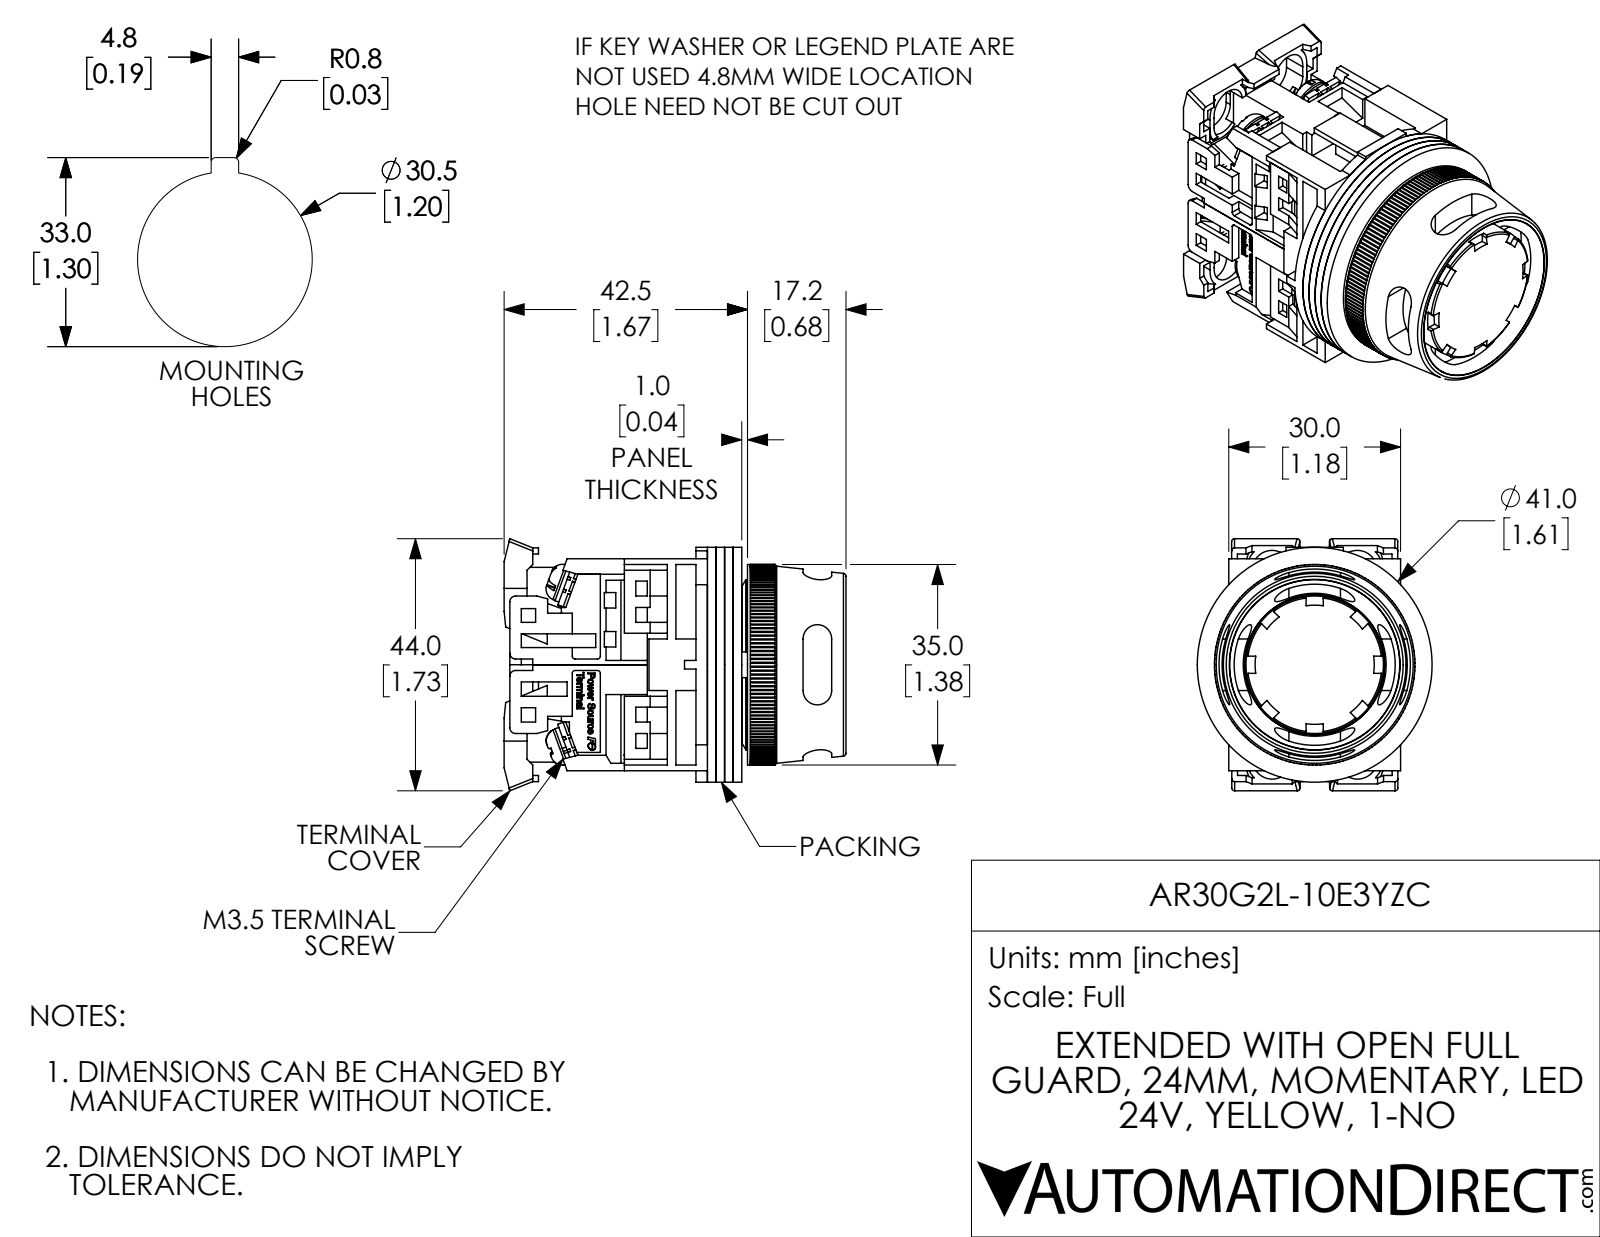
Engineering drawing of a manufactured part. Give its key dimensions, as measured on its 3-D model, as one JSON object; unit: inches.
{"part_name": "AR30G2L-10E3YZC", "step_written_by": "SolidWorks 2017 (AUTOMOTIVE_DESIGN)", "units": "inches", "bodies": {"solids": 25, "faces": 2179, "planar": 1508, "cylindrical": 458, "other": 213}, "overall_size": [2.35, 1.732, 1.614], "volume_in3": 2.142, "surface_area_in2": 62.62, "round_holes": [[0.138, 8], [0.142, 4], [0.118, 1], [0.472, 1], [0.709, 1], [0.728, 1], [0.787, 1], [0.945, 1], [1.252, 1]], "round_bosses_or_shafts": [[0.26, 4], [0.138, 4], [1.614, 1], [1.378, 1], [1.181, 1], [0.866, 1], [0.776, 1], [0.551, 1]], "partial_cylinders_radius": [[0.01, 160], [0.012, 16], [0.059, 16], [0.02, 12], [0.039, 4], [0.098, 4], [0.138, 4], [0.177, 4]], "face_to_face_distances": [0.059, 0.118, 0.039, 0.177, 0.276, 1.417, 0.728, 0.811, 0.079, 1.358], "hole_center_spacings": [0.579, 0.61]}
